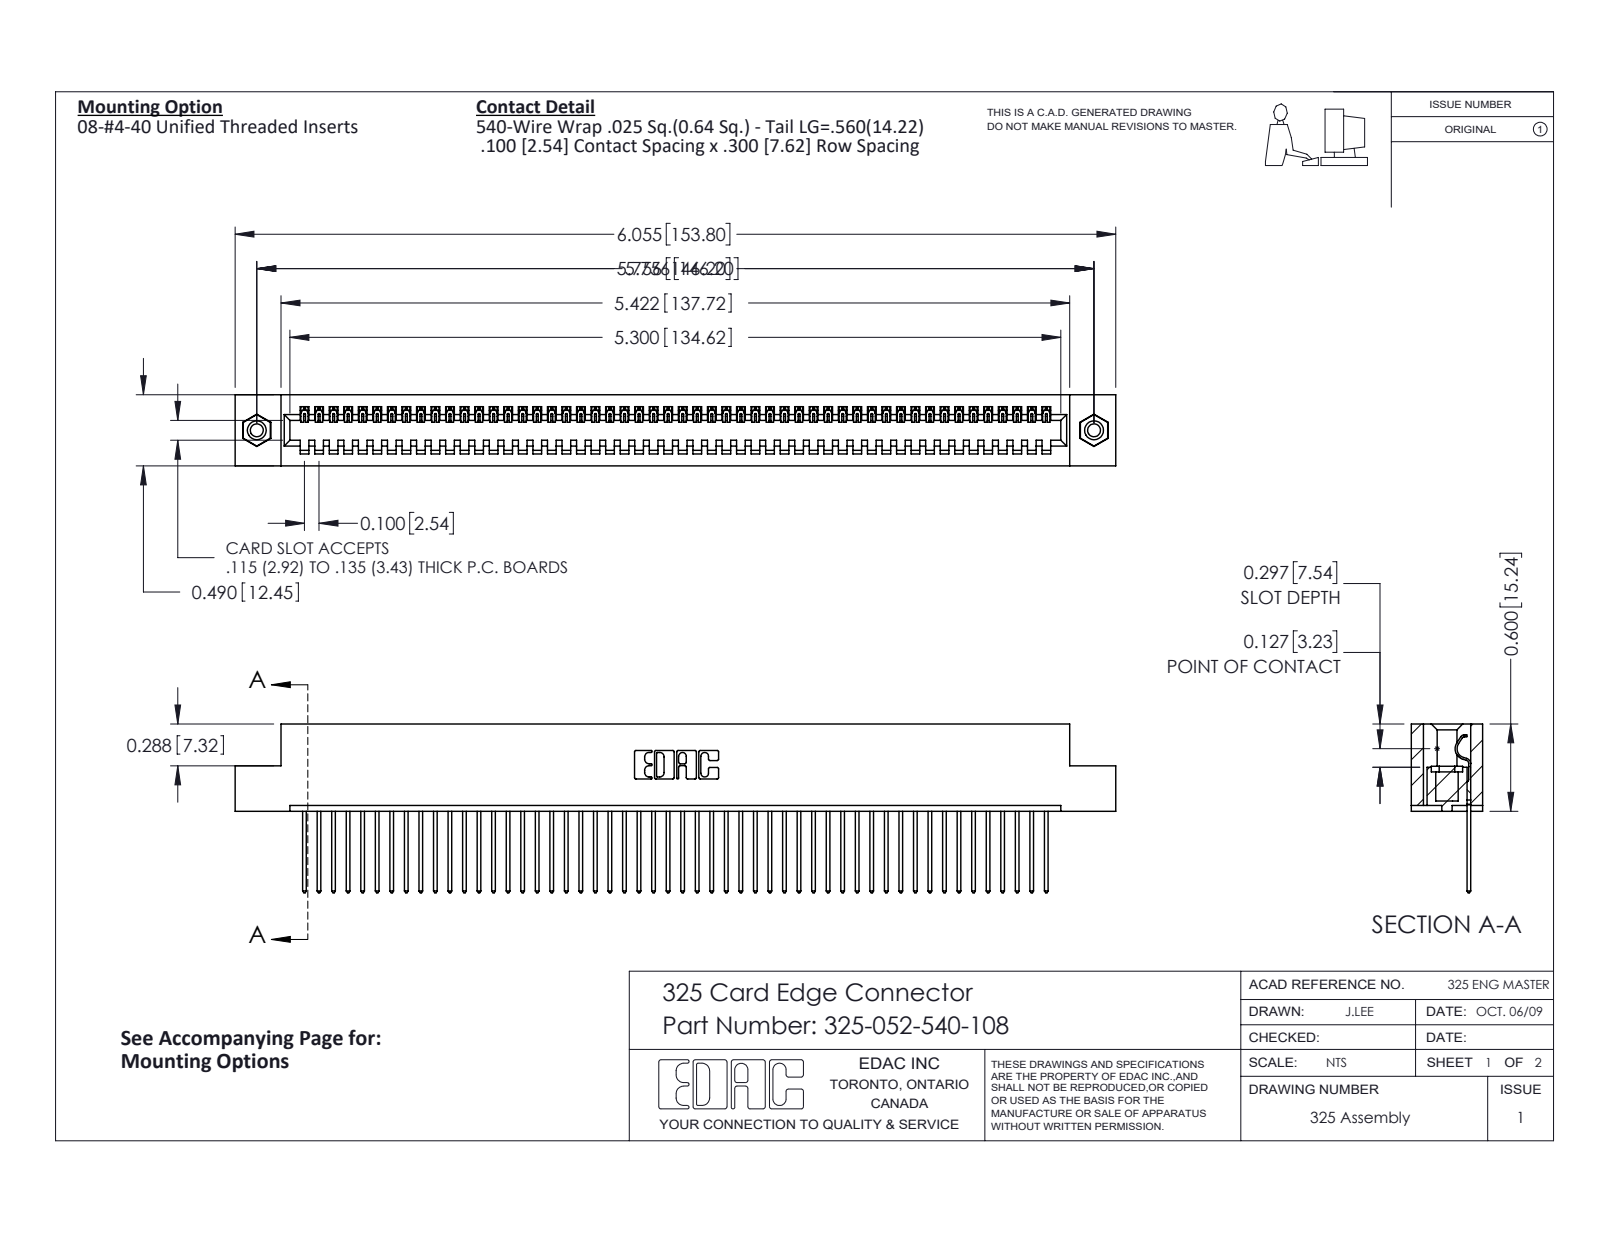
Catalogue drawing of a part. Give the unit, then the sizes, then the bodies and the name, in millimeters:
Units: millimetres
Overall size (bounding box): 153.8 × 29.5 × 12.4
Round holes (diameter × count): ⌀2.3 ×2, ⌀3.2 ×2, ⌀4.1 ×2
Round bosses / shafts (diameter × count): ⌀3.9 ×2
Partial cylindrical surfaces — rounded edges, fillets, slot ends (radius × count): R0.2 ×104, R0.3 ×104, R0.3 ×22, R0.2 ×6, R0.8 ×6, R0.7 ×3, R0.4 ×1, R0.6 ×1
Main face-to-face distances: 2.1, 10.3, 12.4, 7.6, 2.7, 9.7, 0.6, 8.3, 14.2, 6.7
Hole centre spacings: 146.2
Volume: 19 660 mm³ · Surface area: 22 190 mm²
Bodies: 55 solids, 3190 faces (2286 planar, 888 cylindrical, 16 other)
Part name (STEP PRODUCT): 325-292-001_325-293-140; 345-250-001_345-250-003-102; 325-052-540-108; 325 Part_TI
STEP written by: SolidWorks 2016 (CONFIG_CONTROL_DESIGN)
